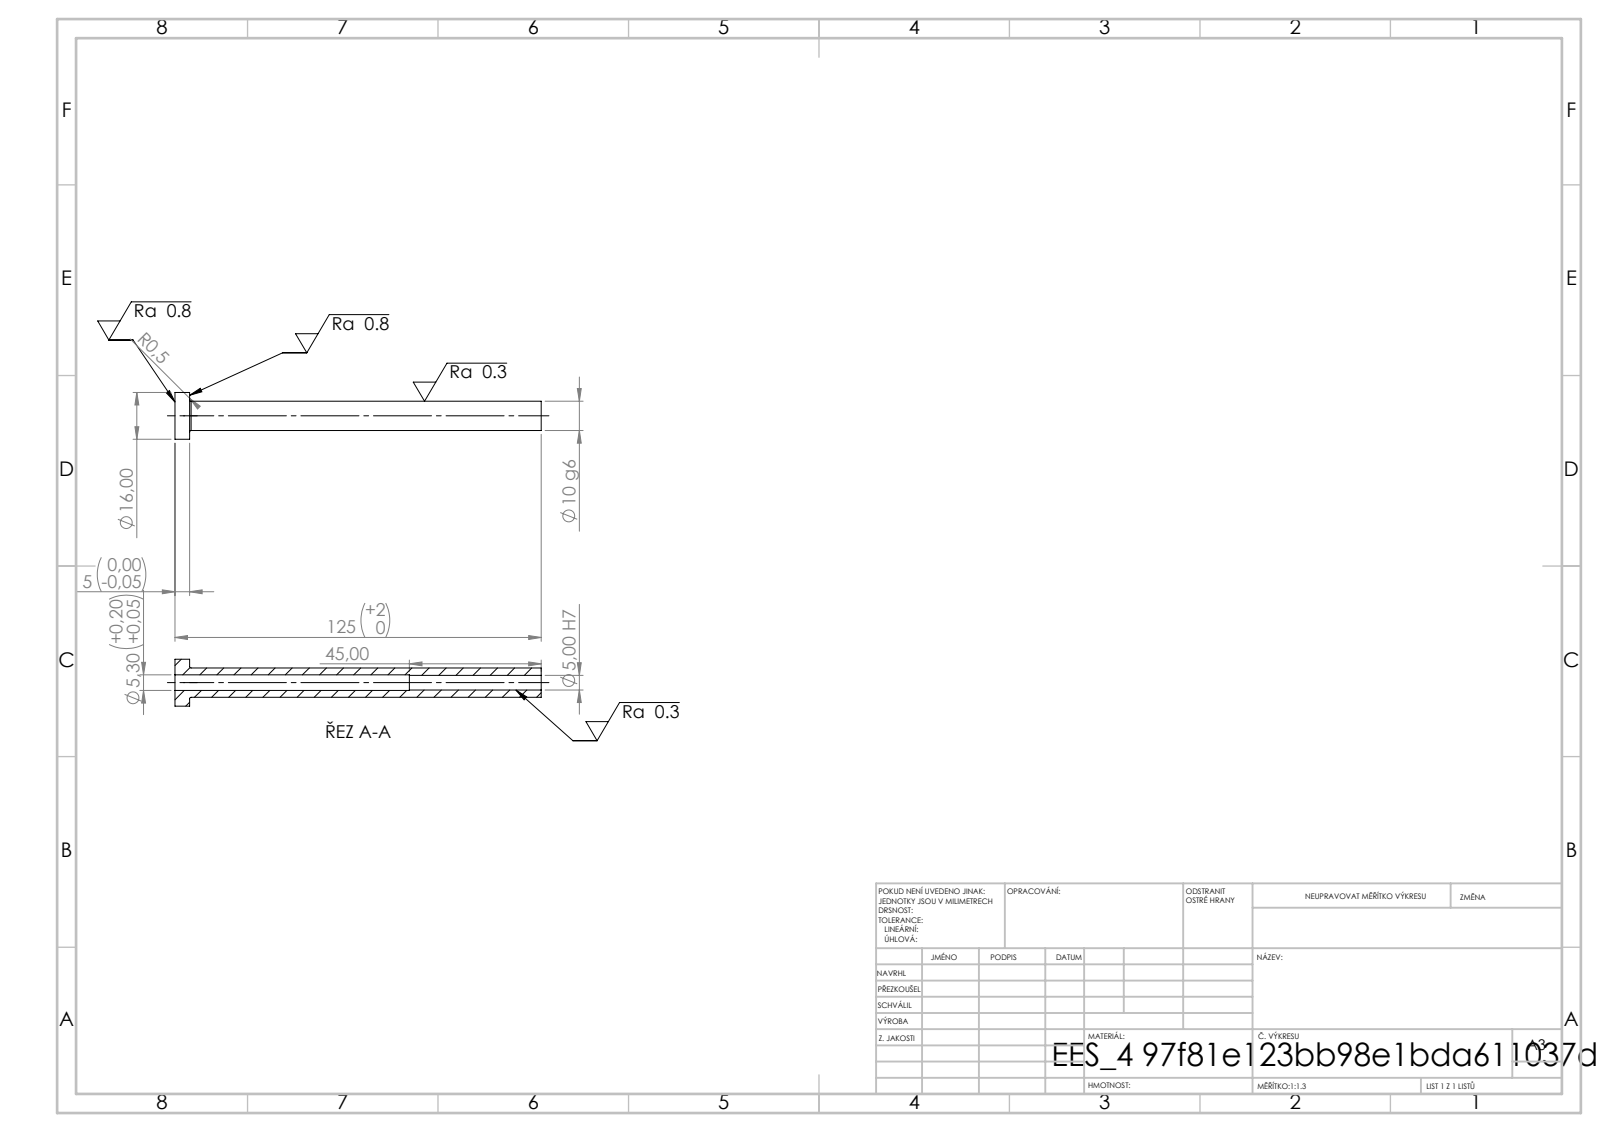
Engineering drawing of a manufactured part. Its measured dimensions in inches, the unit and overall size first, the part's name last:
Units: inches
Overall size (bounding box): 4.921 × 0.63 × 0.63
Round holes (diameter × count): ⌀0.197 ×1, ⌀0.209 ×1
Round bosses / shafts (diameter × count): ⌀0.63 ×1, ⌀0.394 ×1
Main face-to-face distances: 0.197, 4.921, 4.724, 3.15, 2.953, 1.772
Volume: 0.475 in³ · Surface area: 9.945 in²
Bodies: 1 solid, 14 faces (4 planar, 8 cylindrical, 2 other)
STEP written by: SolidWorks 2019 (CONFIG_CONTROL_DESIGN)
